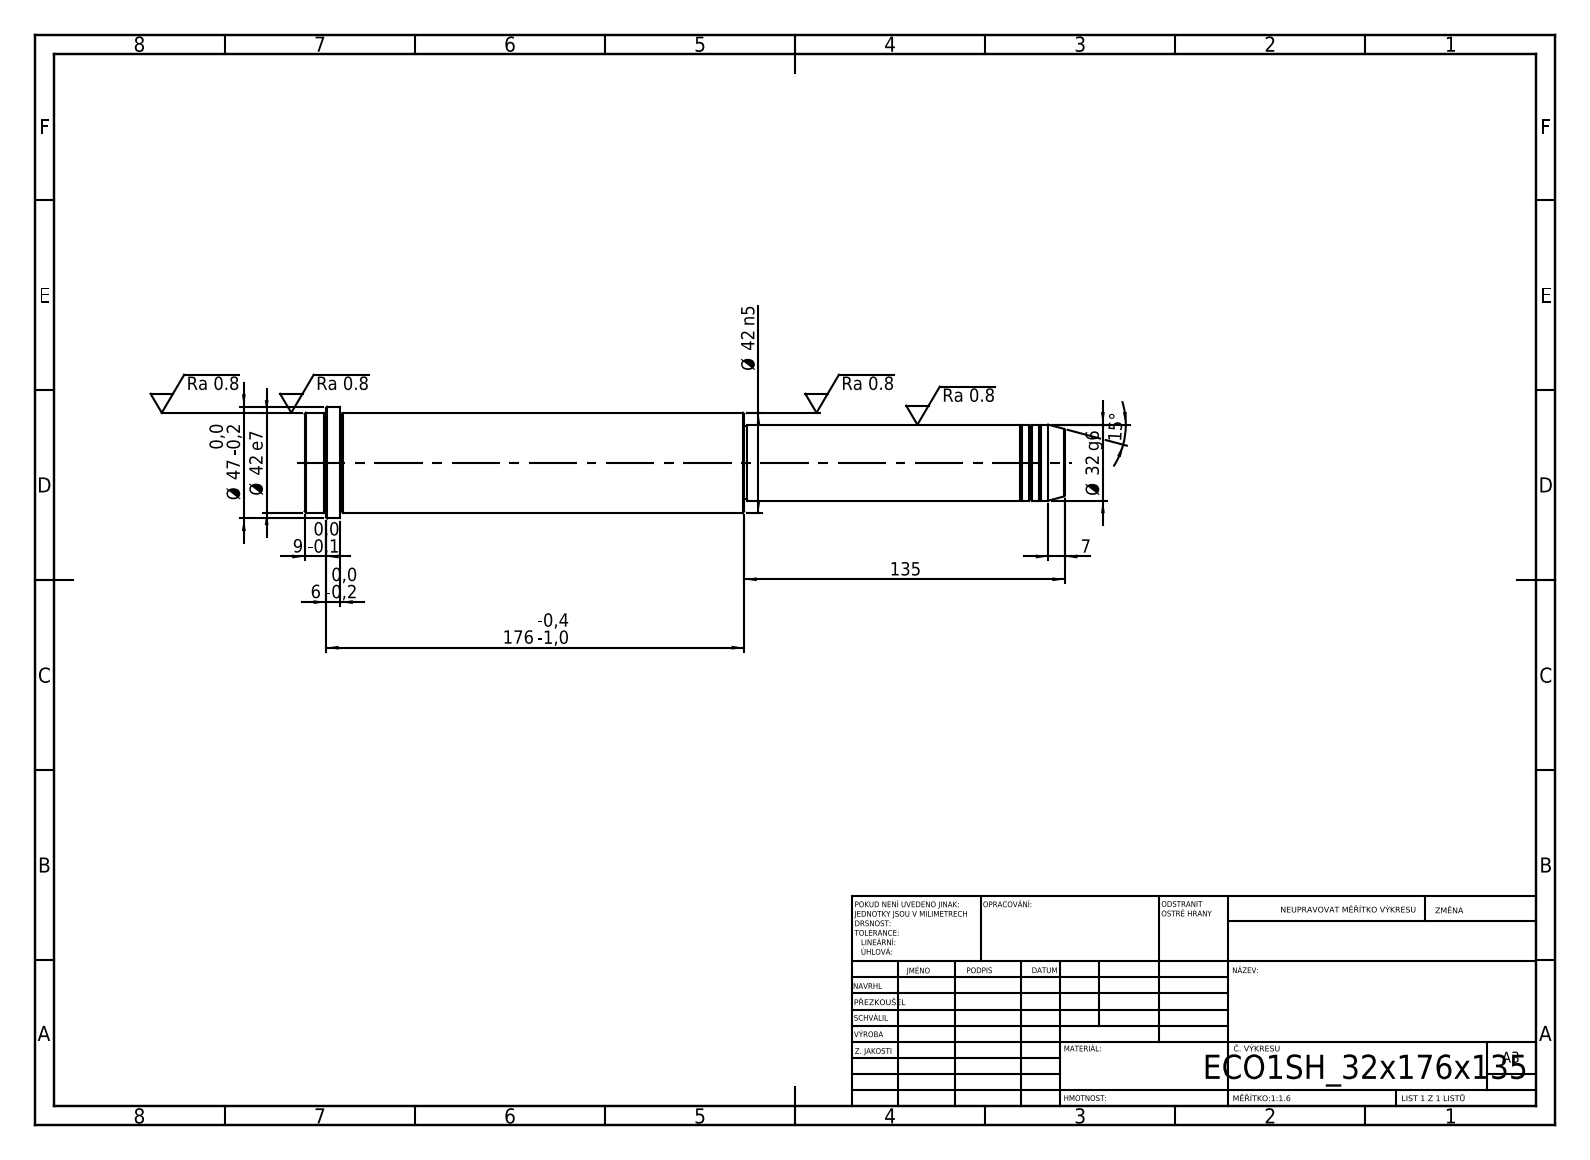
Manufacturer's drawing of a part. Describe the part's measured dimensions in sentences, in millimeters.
Its 3-D file was written by "SolidWorks 2019 (CONFIG_CONTROL_DESIGN)". It is 1 solid with 52 faces: 6 planar, 16 cylindrical and 30 other. Overall it measures 320 by 47 by 47 millimeters. Its volume is 366 021 cubic millimeters and its surface area 41 622 square millimeters. Round bosses or shafts: 1 of diameter 47, 1 of diameter 42, 1 of diameter 32, 1 of diameter 31. The main face-to-face distances are 320, 135, 185, 305, 170, 15, 311, 176, 6, 9.
